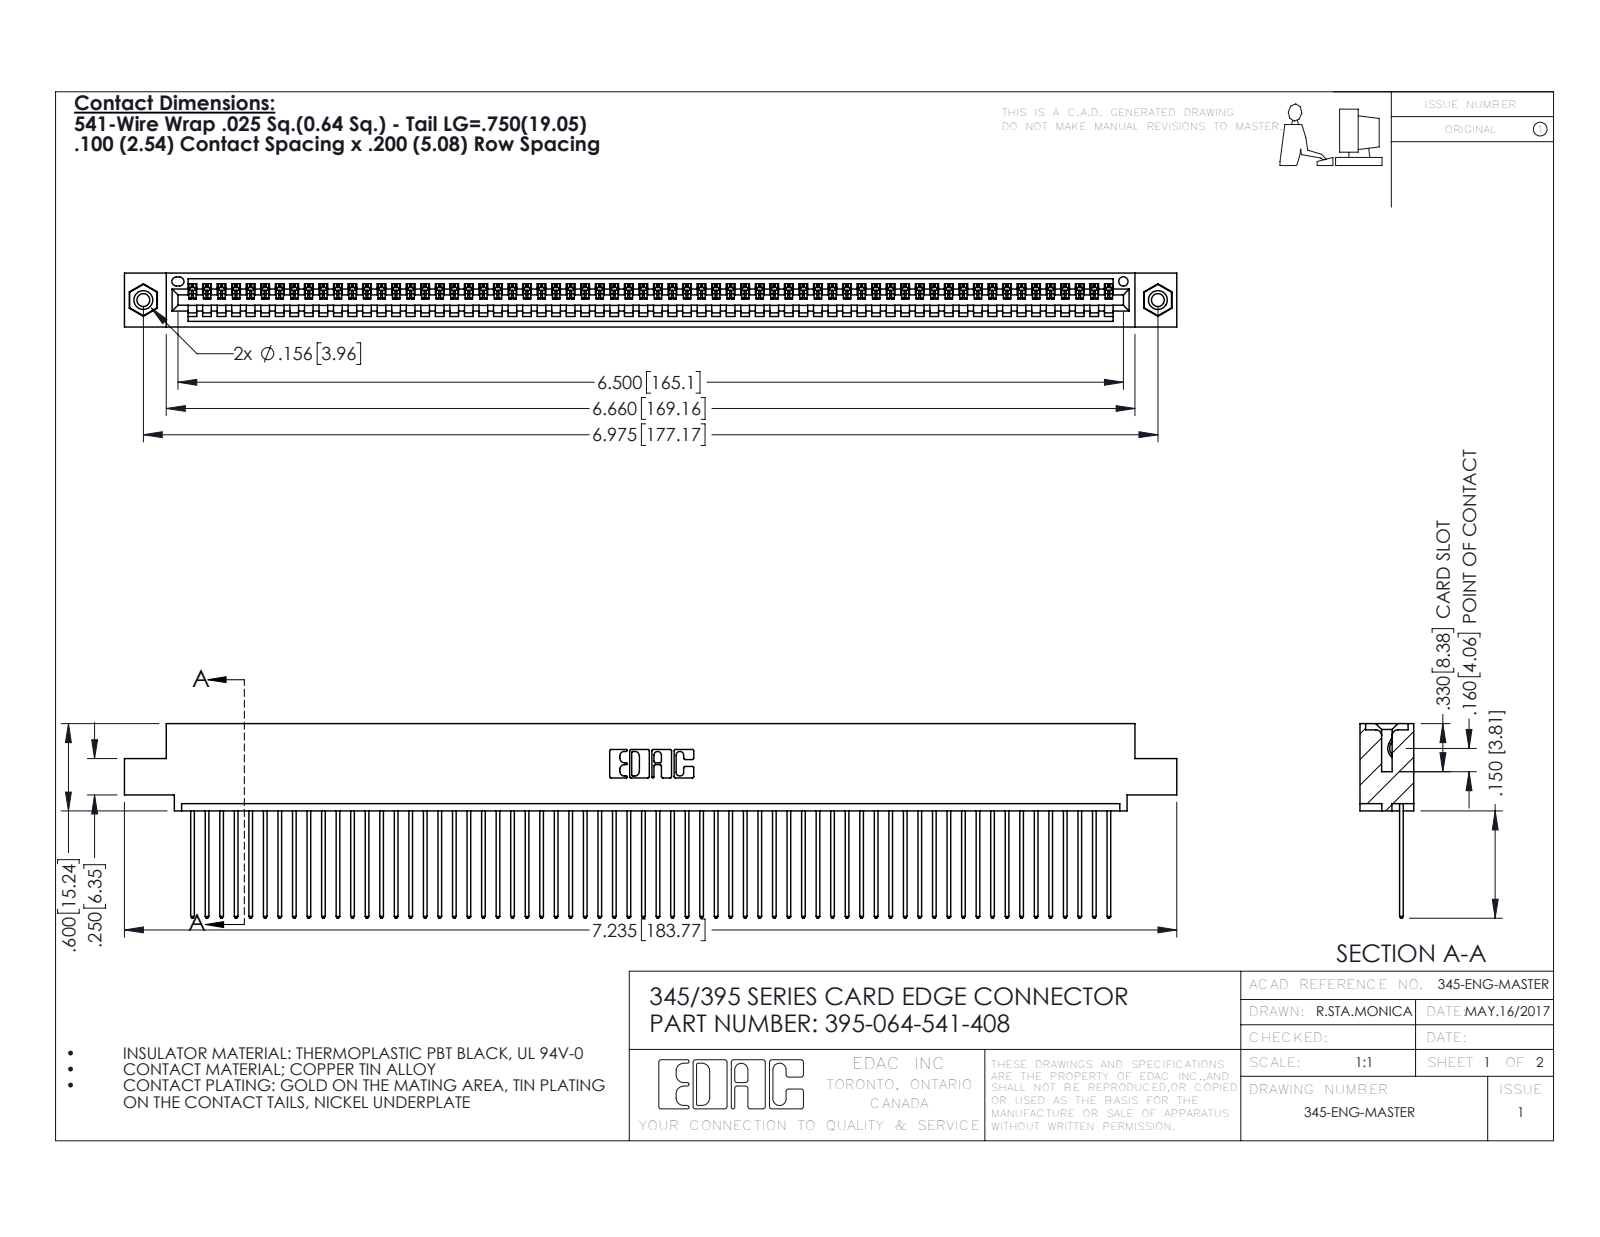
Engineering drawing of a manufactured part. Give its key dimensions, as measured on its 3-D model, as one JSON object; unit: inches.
{"part_name": "395-064-541-408; 345-250-001_345-250-003-102; 345-292-001_345-293-141; 345 Part_0.110 Offset - 0.156 Dia-TI", "step_written_by": "SolidWorks 2016 (CONFIG_CONTROL_DESIGN)", "units": "inches", "bodies": {"solids": 67, "faces": 3902, "planar": 2676, "cylindrical": 1210, "other": 16}, "overall_size": [7.235, 1.337, 0.37], "volume_in3": 1.084, "surface_area_in2": 39.14, "round_holes": [[0.089, 2], [0.125, 2], [0.156, 2], [0.064, 1]], "round_bosses_or_shafts": [[0.155, 2]], "partial_cylinders_radius": [[0.006, 128], [0.01, 128], [0.01, 22], [0.007, 6], [0.031, 6], [0.026, 3], [0.031, 2], [0.04, 2]], "face_to_face_distances": [0.072, 0.298, 0.098, 0.272, 0.025, 0.37, 0.2, 0.225, 0.149, 0.072], "hole_center_spacings": [0.27, 6.739, 6.975]}
